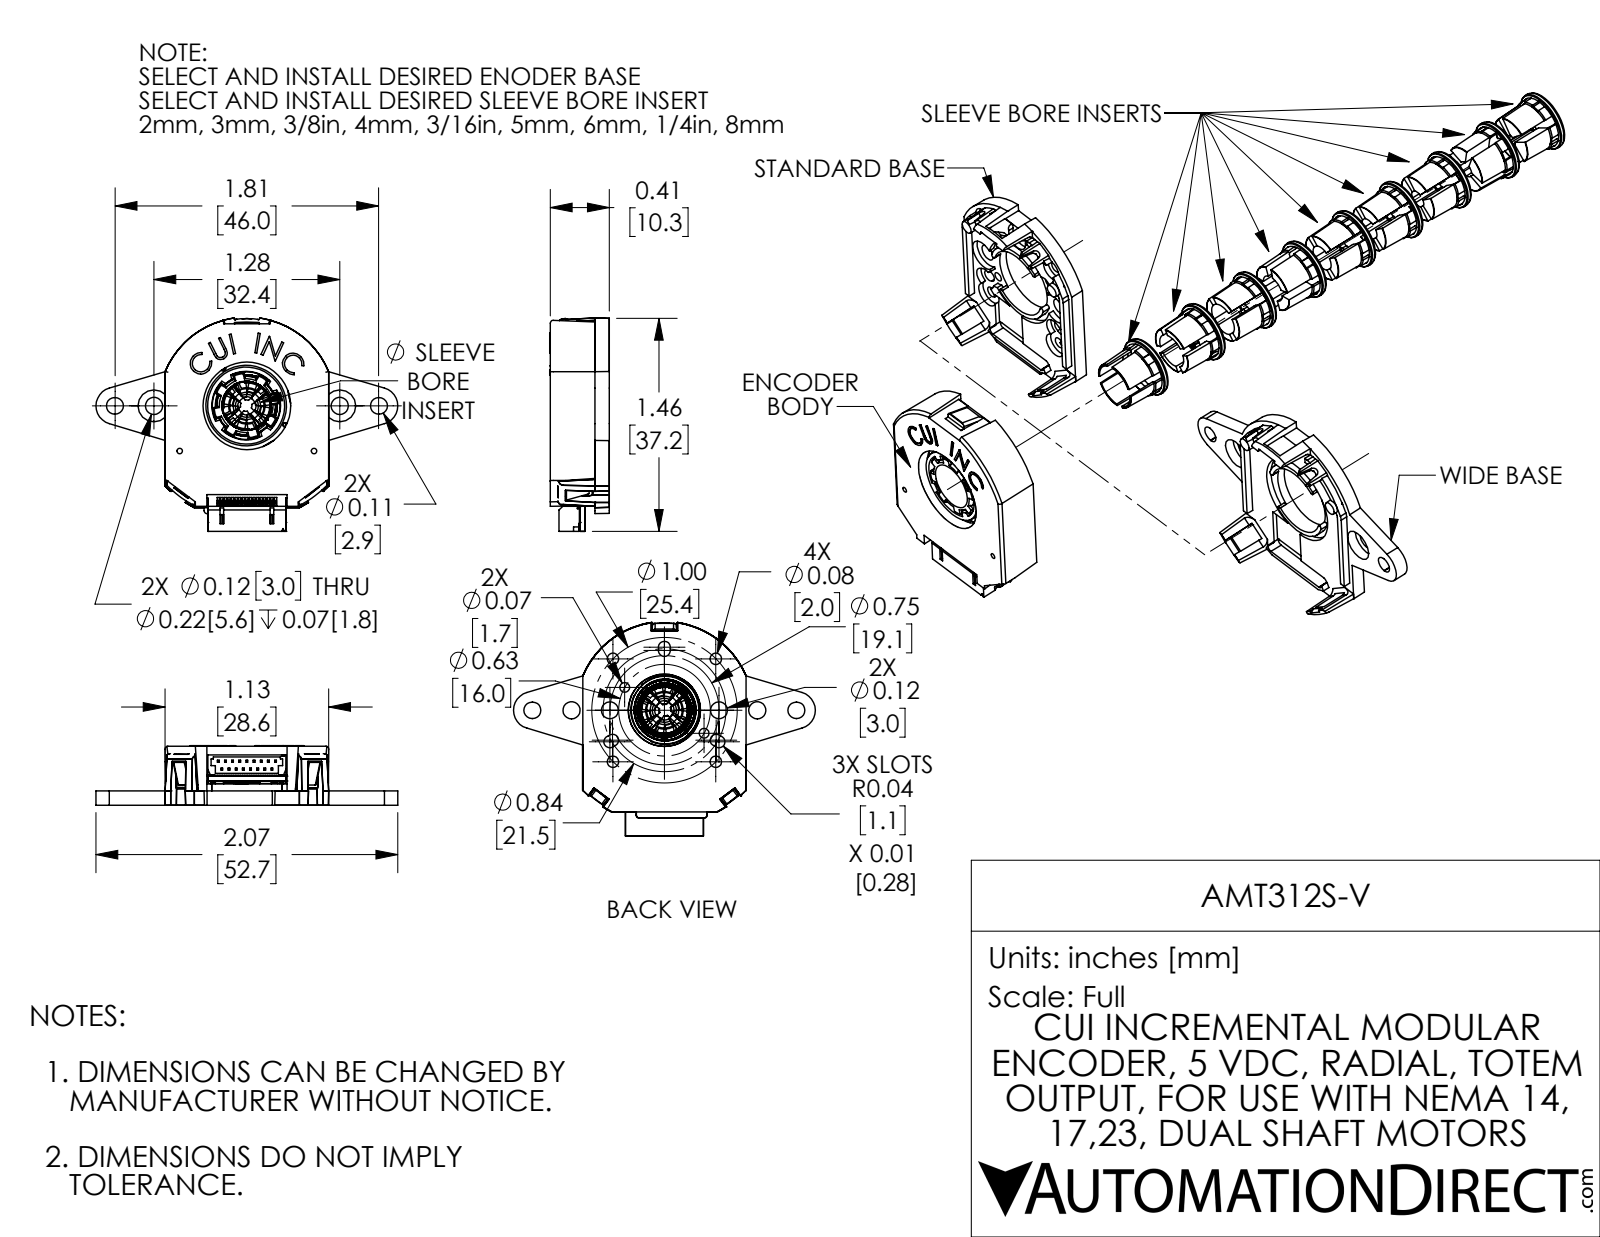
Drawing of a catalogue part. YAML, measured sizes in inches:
part_name: "AMT312S-V"
step_written_by: "SolidWorks 2021 (AUTOMOTIVE_DESIGN)"
units: inches
bodies: {solids: 16, faces: 4202, planar: 1922, cylindrical: 1559, other: 721}
overall_size: [5.463, 4.573, 1.467]
volume: 0.564
surface_area: 26.18
round_holes:
  - {diameter: 0.026, count: 168}
  - {diameter: 0.031, count: 4}
  - {diameter: 0.037, count: 4}
  - {diameter: 0.079, count: 4}
  - {diameter: 0.031, count: 2}
  - {diameter: 0.063, count: 2}
  - {diameter: 0.067, count: 2}
  - {diameter: 0.091, count: 2}
  - {diameter: 0.116, count: 2}
  - {diameter: 0.118, count: 2}
  - {diameter: 0.161, count: 2}
  - {diameter: 0.177, count: 2}
round_bosses_or_shafts:
  - {diameter: 0.059, count: 4}
  - {diameter: 0.051, count: 4}
  - {diameter: 0.413, count: 2}
  - {diameter: 0.094, count: 2}
  - {diameter: 0.763, count: 1}
  - {diameter: 0.465, count: 1}
  - {diameter: 0.356, count: 1}
partial_cylinders:
  - {radius: 0.379, count: 64}
  - {radius: 0.039, count: 30}
  - {radius: 0.498, count: 29}
  - {radius: 0.079, count: 11}
  - {radius: 0.016, count: 8}
  - {radius: 0.02, count: 6}
  - {radius: 0.041, count: 6}
  - {radius: 0.012, count: 4}
face_to_face_distances: [0.057, 0.033, 0.098, 1.547, 1.58, 1.604, 1.638, 1.687, 0.156, 1.448]
hole_center_spacings: [0.366, 0.181, 0.278, 0.309, 0.707, 0.068, 0.089, 0.354]
